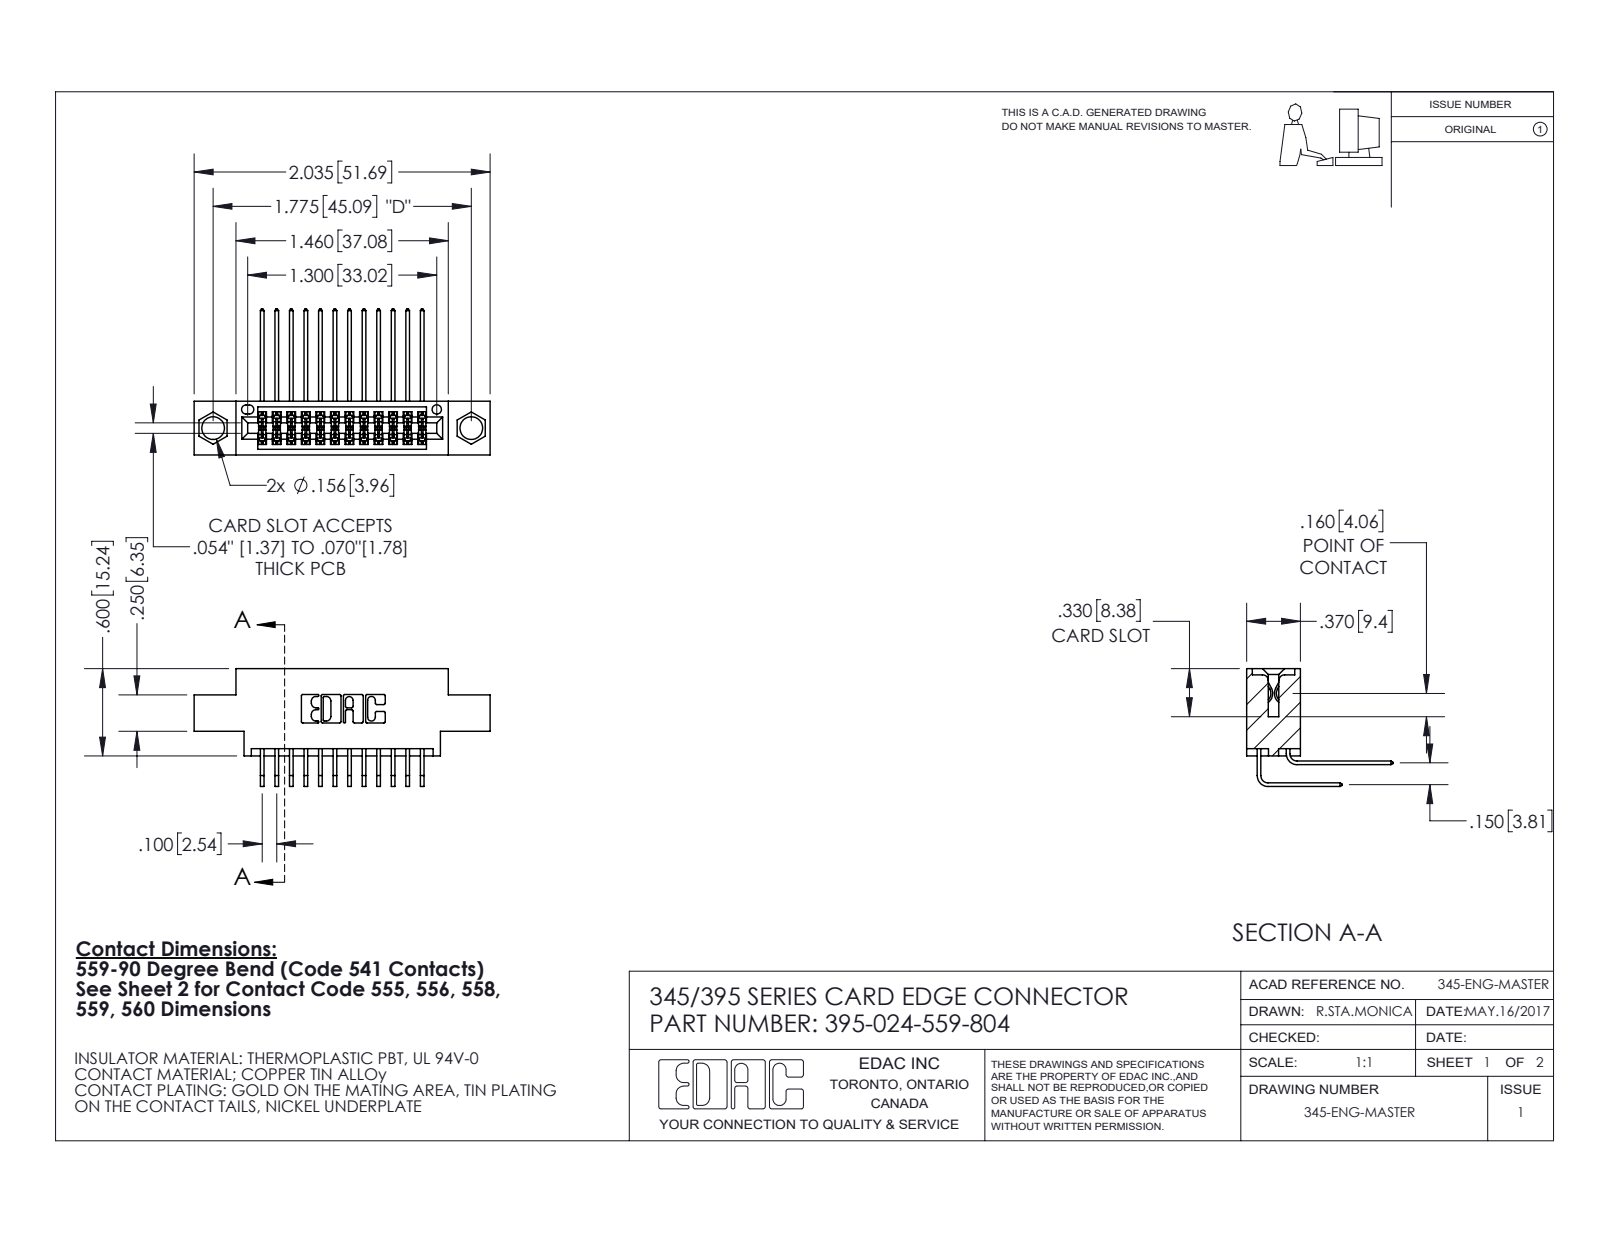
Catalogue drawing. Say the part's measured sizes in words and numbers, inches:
The part is named "345-292-001_558 559 Tail - 1; 345 Part_0.170 Offset - 0.156 Dia-TI; 395-024-559-804; 345-292-001_559 Tail - 2". Its 3-D file was written by "SolidWorks 2020 (CONFIG_CONTROL_DESIGN)". It is 25 solids with 1392 faces: 938 planar, 454 cylindrical and 0 other. Overall it measures 2.035 by 1.005 by 0.809 inches. Its volume is 0.284 cubic inches and its surface area 10.78 square inches. Round holes: 2 of diameter 0.156, 1 of diameter 0.064. Partial cylindrical surfaces (rounded edges, fillets, slot ends): 36 of radius 0.006, 22 of radius 0.01, 6 of radius 0.007, 6 of radius 0.031, 3 of radius 0.026, 2 of radius 0.014, 2 of radius 0.019, 2 of radius 0.022. The main face-to-face distances are 0.072, 0.298, 0.37, 0.2, 0.098, 0.272, 0.025, 0.15, 0.225, 0.175. The hole center spacings are 0.27, 1.543, 1.775.
